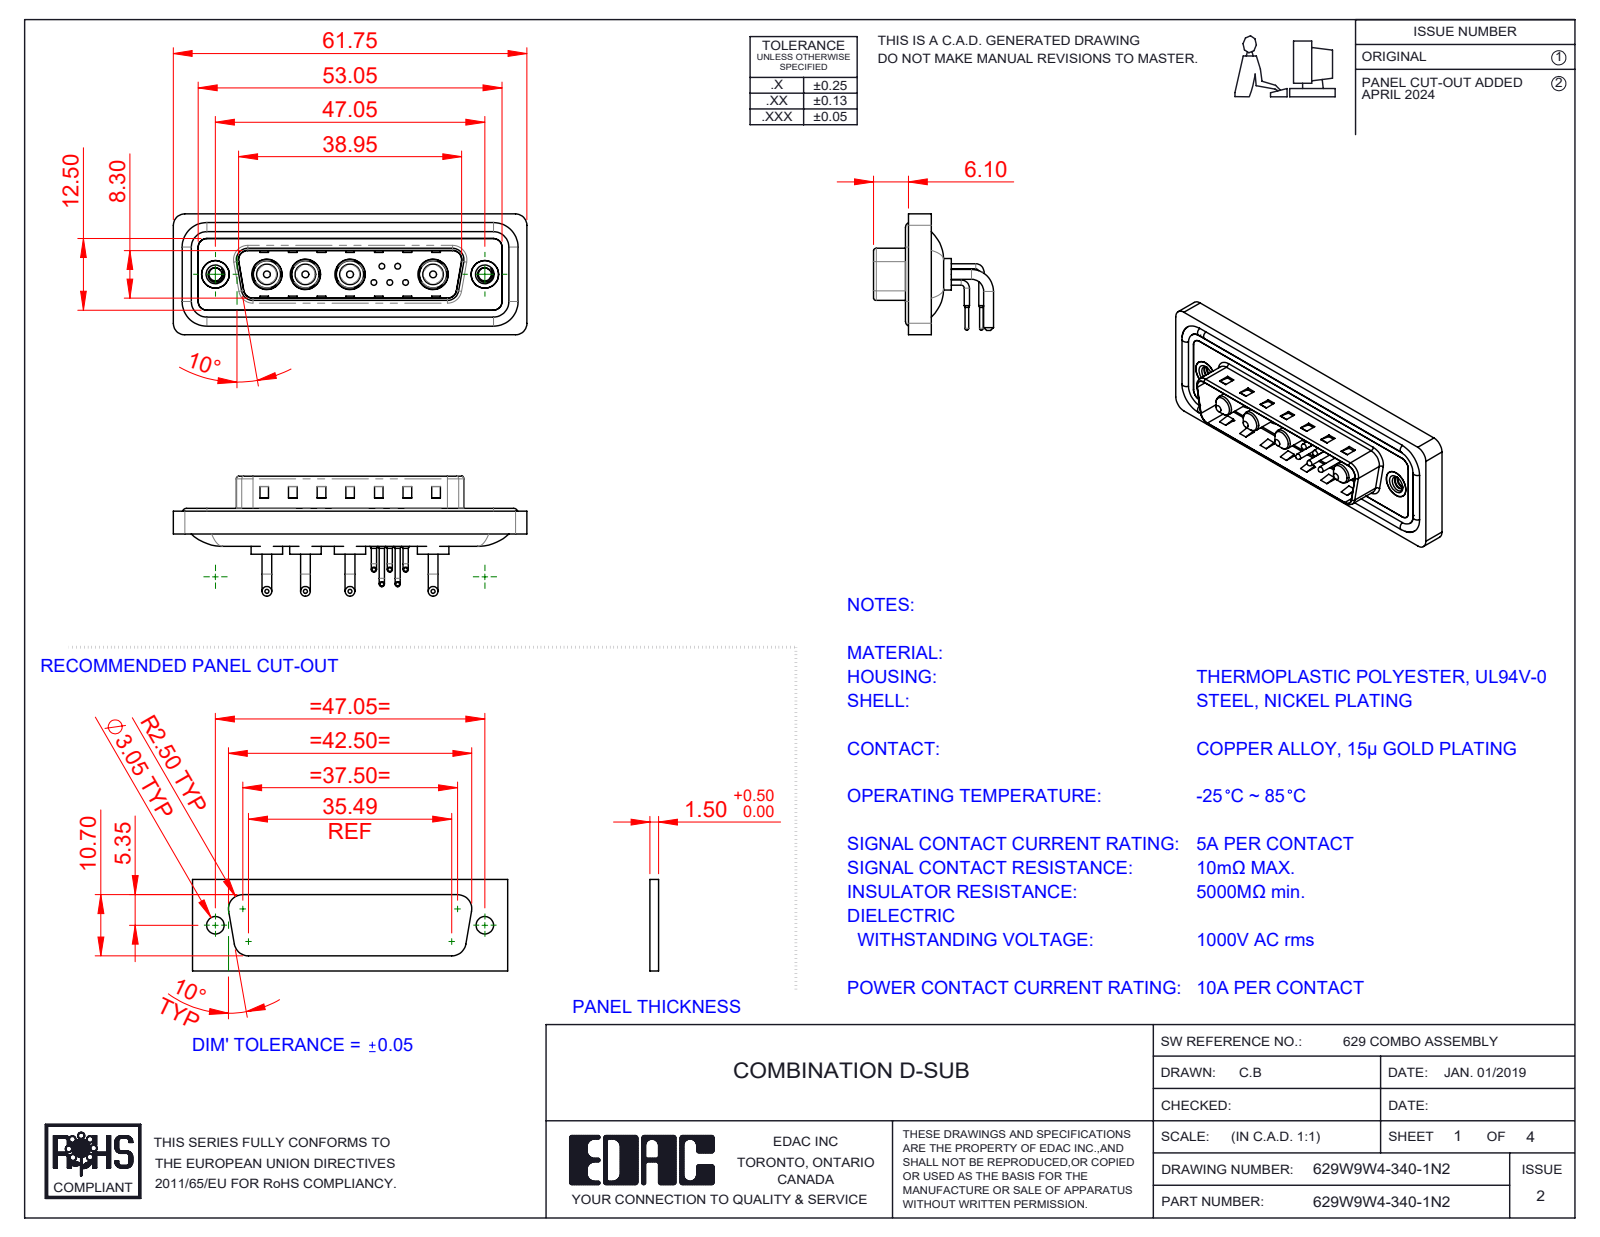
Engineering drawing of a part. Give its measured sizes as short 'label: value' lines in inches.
name: Power Pin_10A RA; 629Combo Contact Row 1; 629Combo Housing_9W4; 629Combo Shell Rear_25 Contacts (+5 more)
written by: SolidWorks 2023 (CONFIG_CONTROL_DESIGN)
unit: in
bodies: 20 solids, 1205 faces (569 planar, 452 cylindrical, 184 other)
size: 2.431 × 0.831 × 0.825
volume: 0.457 in³; area: 18.87 in²
holes: 5× ⌀0.03, 5× ⌀0.063, 5× ⌀0.079, 4× ⌀0.191, 4× ⌀0.209, 2× ⌀0.089, 2× ⌀0.157, 2× ⌀0.189, 2× ⌀0.197
bosses: 10× ⌀0.035, 8× ⌀0.067, 5× ⌀0.059, 5× ⌀0.039, 5× ⌀0.026, 4× ⌀0.217, 4× ⌀0.205, 4× ⌀0.187
rounds: 18× R0.059, 18× R0.079, 8× R0.02, 8× R0.063, 5× R0.04, 4× R0.01, 4× R0.024, 4× R0.026
face distances: 0.016, 0.114, 0.031, 0.161, 0.043, 0.177, 0.083, 0.059, 0.063, 0.122
hole spacings: 0.124, 0.109, 0.198, 0.571, 0.109, 0.173, 0.174, 0.197
